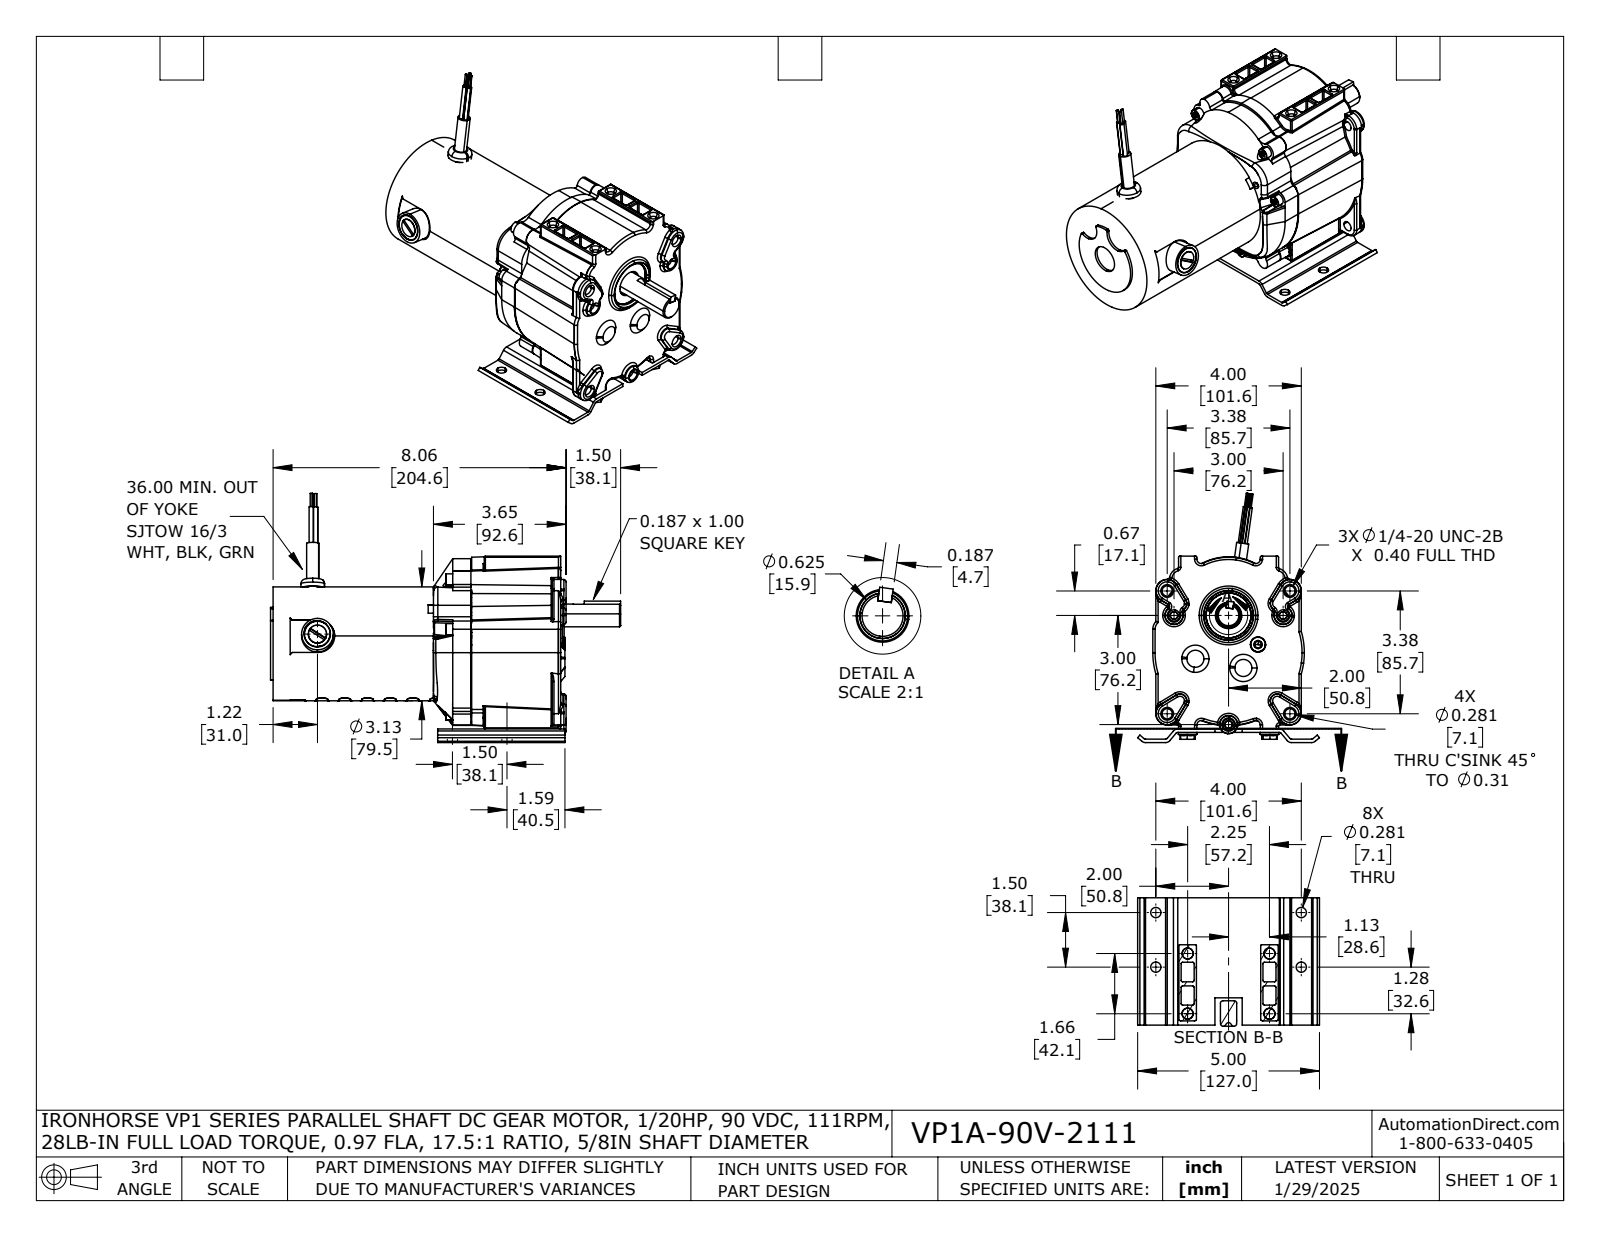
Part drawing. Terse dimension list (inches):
name: VP1A-90V-2111
written by: SolidWorks 2024 (AUTOMOTIVE_DESIGN)
unit: in
bodies: 8 solids, 2435 faces (642 planar, 688 cylindrical, 1105 other)
size: 9.627 × 6.854 × 5
volume: 82.44 in³; area: 303.9 in²
holes: 12× ⌀0.281, 5× ⌀0.218, 3× ⌀0.207, 2× ⌀0.135, 2× ⌀0.159, 2× ⌀0.166, 2× ⌀0.204, 2× ⌀0.397, 2× ⌀0.688, 1× ⌀0.75, 1× ⌀0.813, 1× ⌀0.875
bosses: 5× ⌀0.307, 5× ⌀0.19, 4× ⌀0.51, 4× ⌀0.3, 3× ⌀0.12, 3× ⌀0.06, 2× ⌀0.873, 2× ⌀0.733
rounds: 52× R0.03, 38× R0.031, 22× R0.062, 18× R0.12, 13× R0.156, 10× R0.19, 8× R0.05, 7× R0.06
face distances: 2.449, 3.5, 1.051, 0.095, 0.095, 7.91, 5.461, 4.41, 0.13, 0.28
hole spacings: 1.5, 1.691, 0.698, 0.952, 1.224, 1.426, 1.552, 1.656
